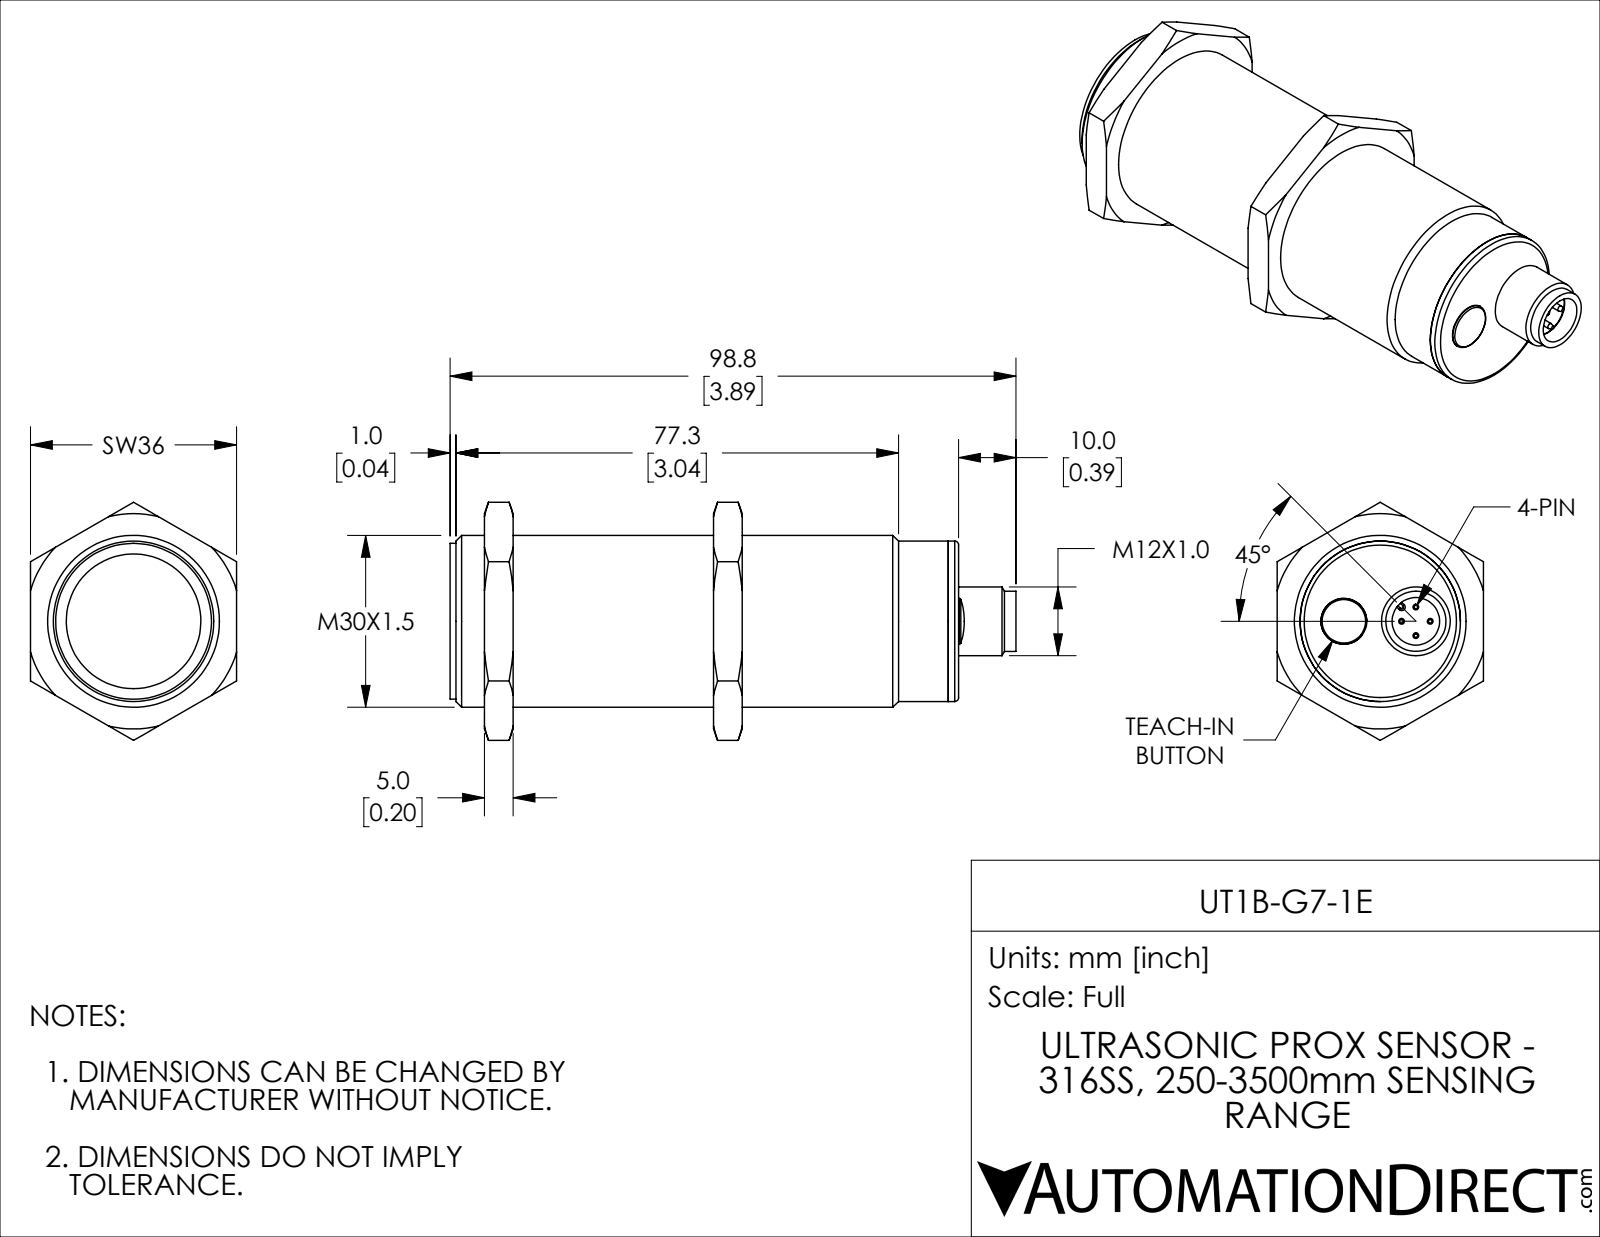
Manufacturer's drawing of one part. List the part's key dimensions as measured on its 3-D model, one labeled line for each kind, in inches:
Part name (STEP PRODUCT): UT1B-G7-1E
STEP written by: SolidWorks 2018 (AUTOMOTIVE_DESIGN)
Units: inches
Bodies: 7 solids, 152 faces (46 planar, 49 cylindrical, 57 other)
Overall size (bounding box): 3.89 × 1.637 × 1.417
Volume: 4.048 in³ · Surface area: 26.65 in²
Round holes (diameter × count): ⌀0.071 ×4, ⌀0.315 ×1, ⌀0.327 ×1, ⌀0.372 ×1, ⌀0.925 ×1, ⌀1.181 ×1
Round bosses / shafts (diameter × count): ⌀0.039 ×4, ⌀1.102 ×1, ⌀1.071 ×1, ⌀0.472 ×1, ⌀0.413 ×1, ⌀0.364 ×1
Partial cylindrical surfaces — rounded edges, fillets, slot ends (radius × count): R0.012 ×2, R0.024 ×1
Main face-to-face distances: 3.386, 0.197, 1.417, 1.772, 1.575, 3.457, 0.039, 3.425, 0.394, 0.071
Hole centre spacings: 0.098, 0.139, 0.197, 0.264, 0.505, 0.146, 0.245, 0.25
